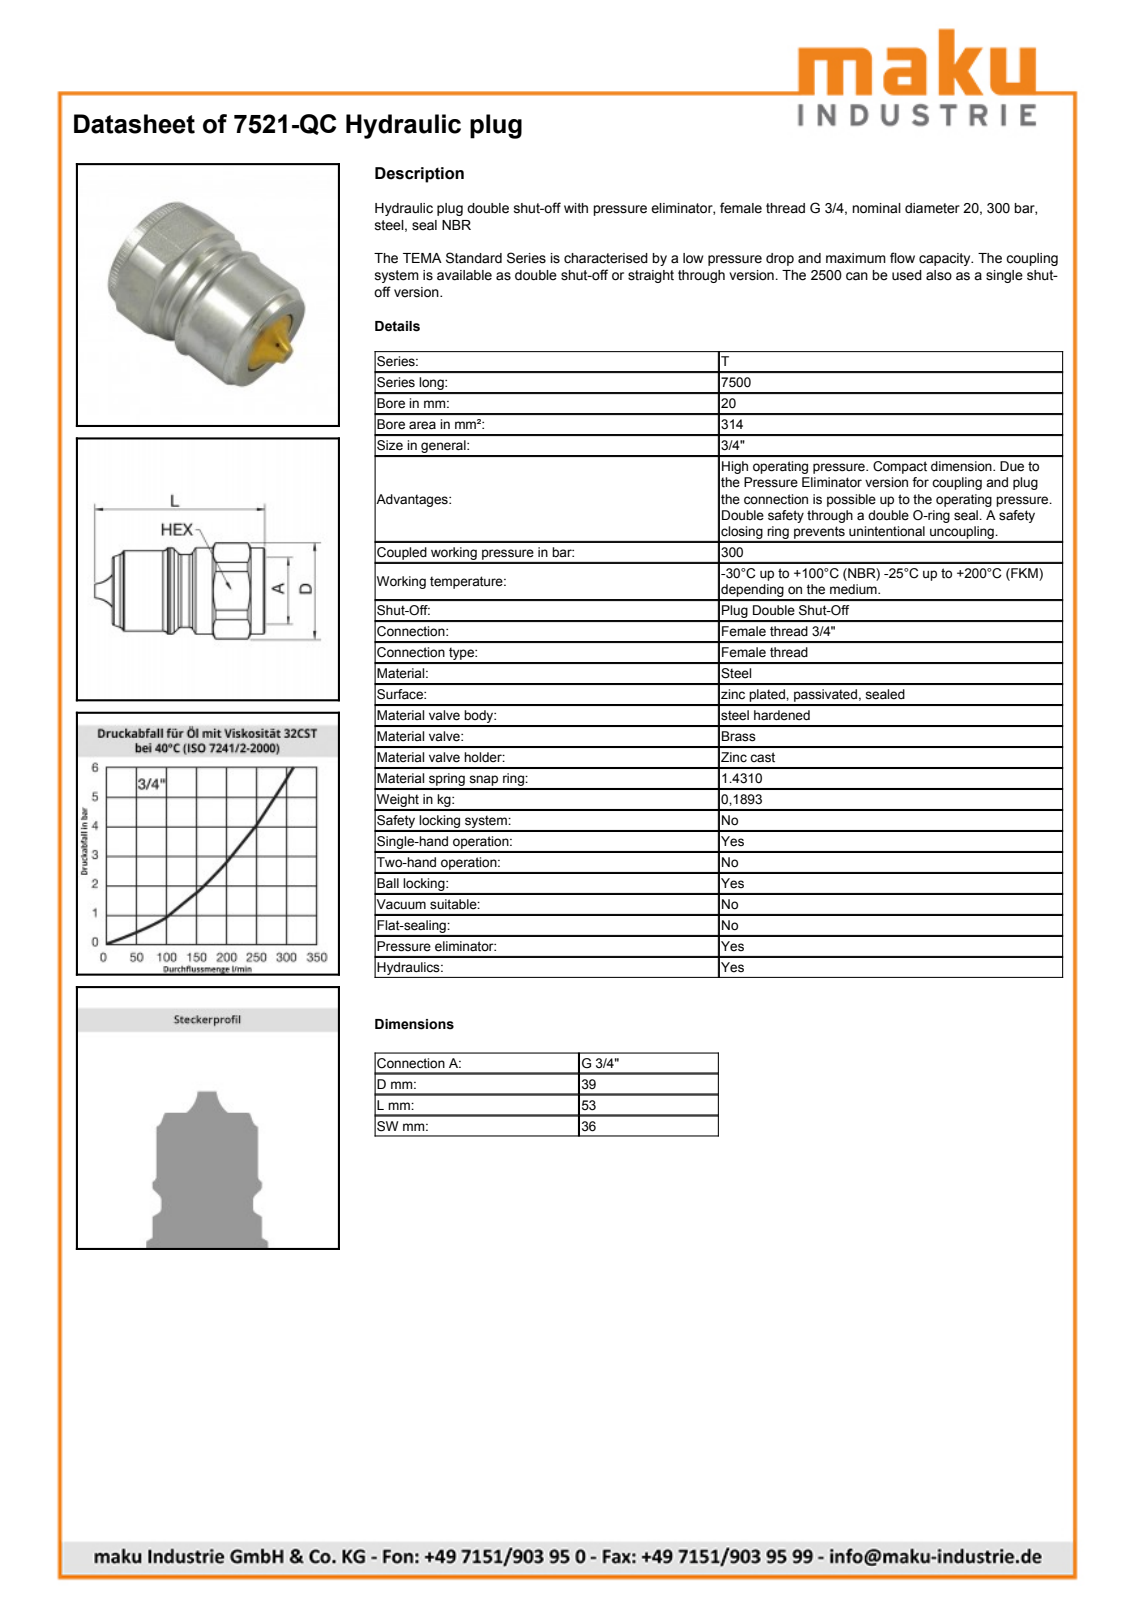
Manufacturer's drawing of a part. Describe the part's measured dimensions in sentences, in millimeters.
The part is named "7521-QC". Its 3-D file was written by "SolidWorks 2009 (AUTOMOTIVE_DESIGN)". It is 1 solid with 77 faces: 13 planar, 22 cylindrical and 42 other. Overall it measures 52.7 by 39 by 35 millimeters. Its volume is 33 205 cubic millimeters and its surface area 8 554 square millimeters. Round holes: 1 of diameter 3.93, 1 of diameter 19, 1 of diameter 24.12. Round bosses or shafts: 1 of diameter 34.7, 1 of diameter 34.6, 1 of diameter 33, 1 of diameter 29.9. Partial cylindrical surfaces (rounded edges, fillets, slot ends): 1 of radius 19.5. The main face-to-face distances are 35, 19.25, 26.75, 46, 6.2, 32.95, 52.2, 6.25, 33, 52.25.
